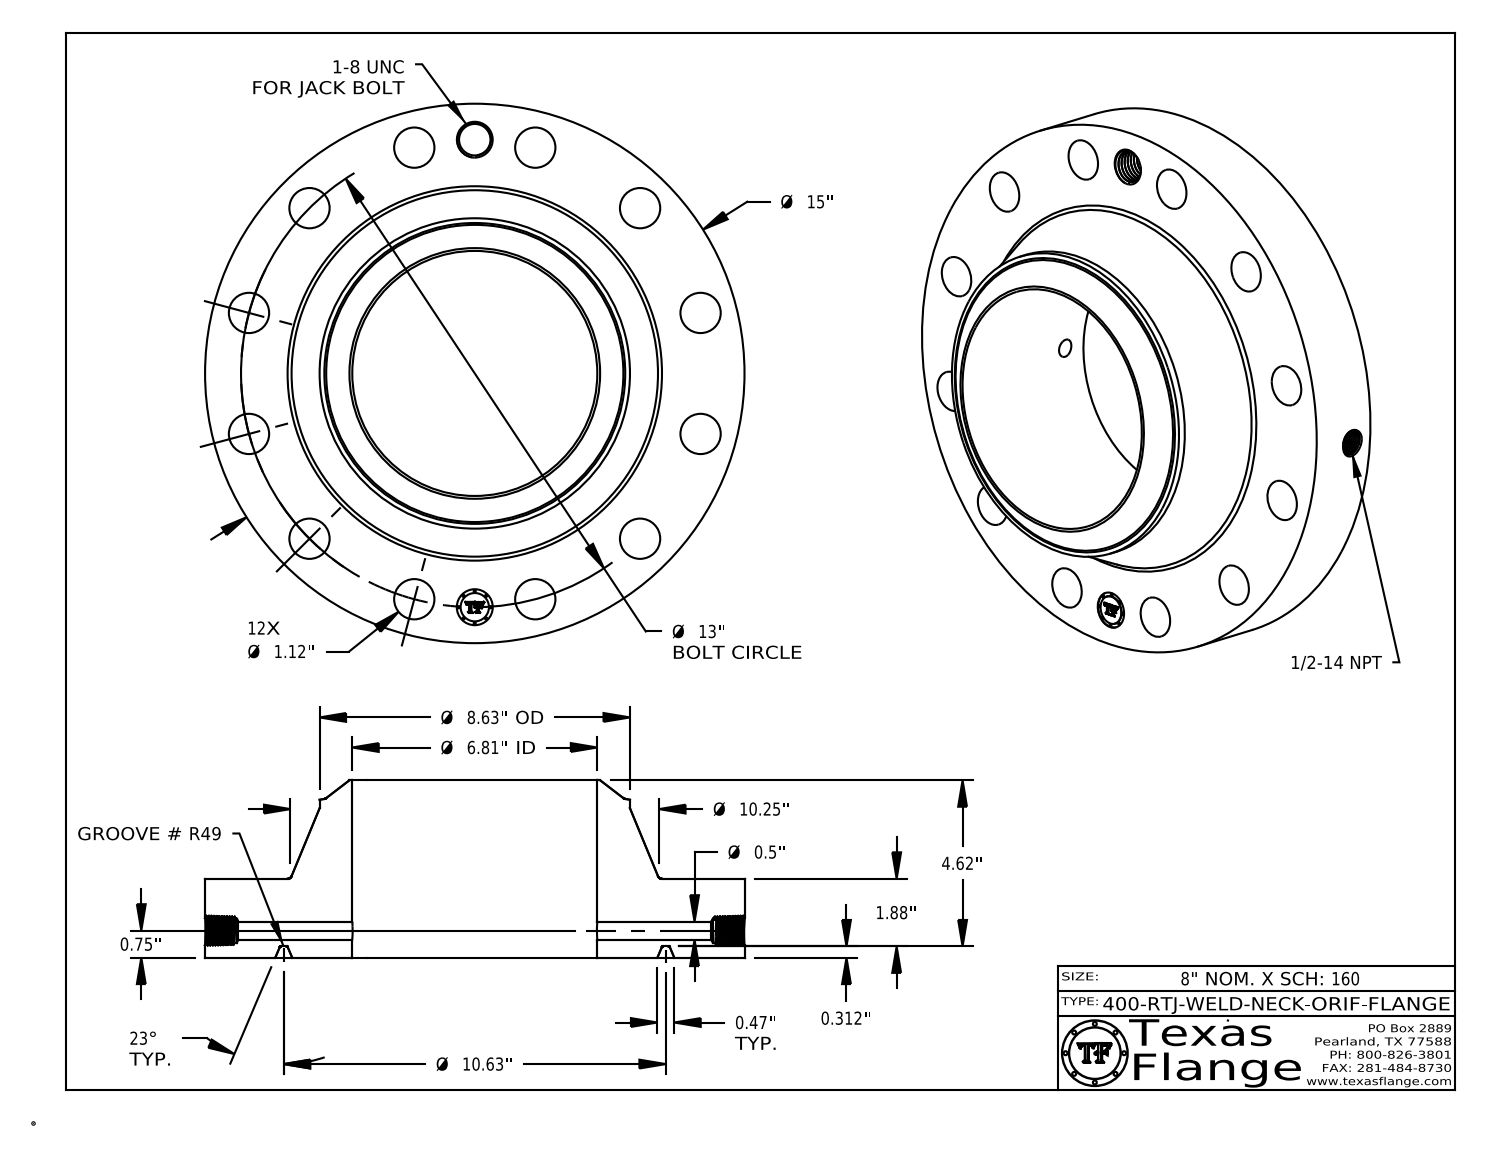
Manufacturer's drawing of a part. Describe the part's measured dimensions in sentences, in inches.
The part is named "400-RTJ-WELD-NECK". Its 3-D file was written by "CATIA V5 STEP AP214 (AUTOMOTIVE_DESIGN)". It is 1 solid with 805 faces: 370 planar, 104 cylindrical and 331 other. Overall it measures 15 by 15 by 4.932 inches. Its volume is 351.3 cubic inches and its surface area 644.8 square inches. Round holes: 12 of diameter 1.12, 1 of diameter 0.5, 1 of diameter 0.672, 1 of diameter 0.875, 1 of diameter 1, 1 of diameter 6.813. Round bosses or shafts: 8 of diameter 0.061, 1 of diameter 15, 1 of diameter 8.63, 1 of diameter 0.788. The main face-to-face distances are 2.192, 0.312, 1.88, 4.932, 4.62, 2.74, 2.177, 1.865, 0.015, 2.755. The hole center spacings are 6.5, 3.365, 9.192, 11.258, 12.557, 13, 1.697, 4.975.
